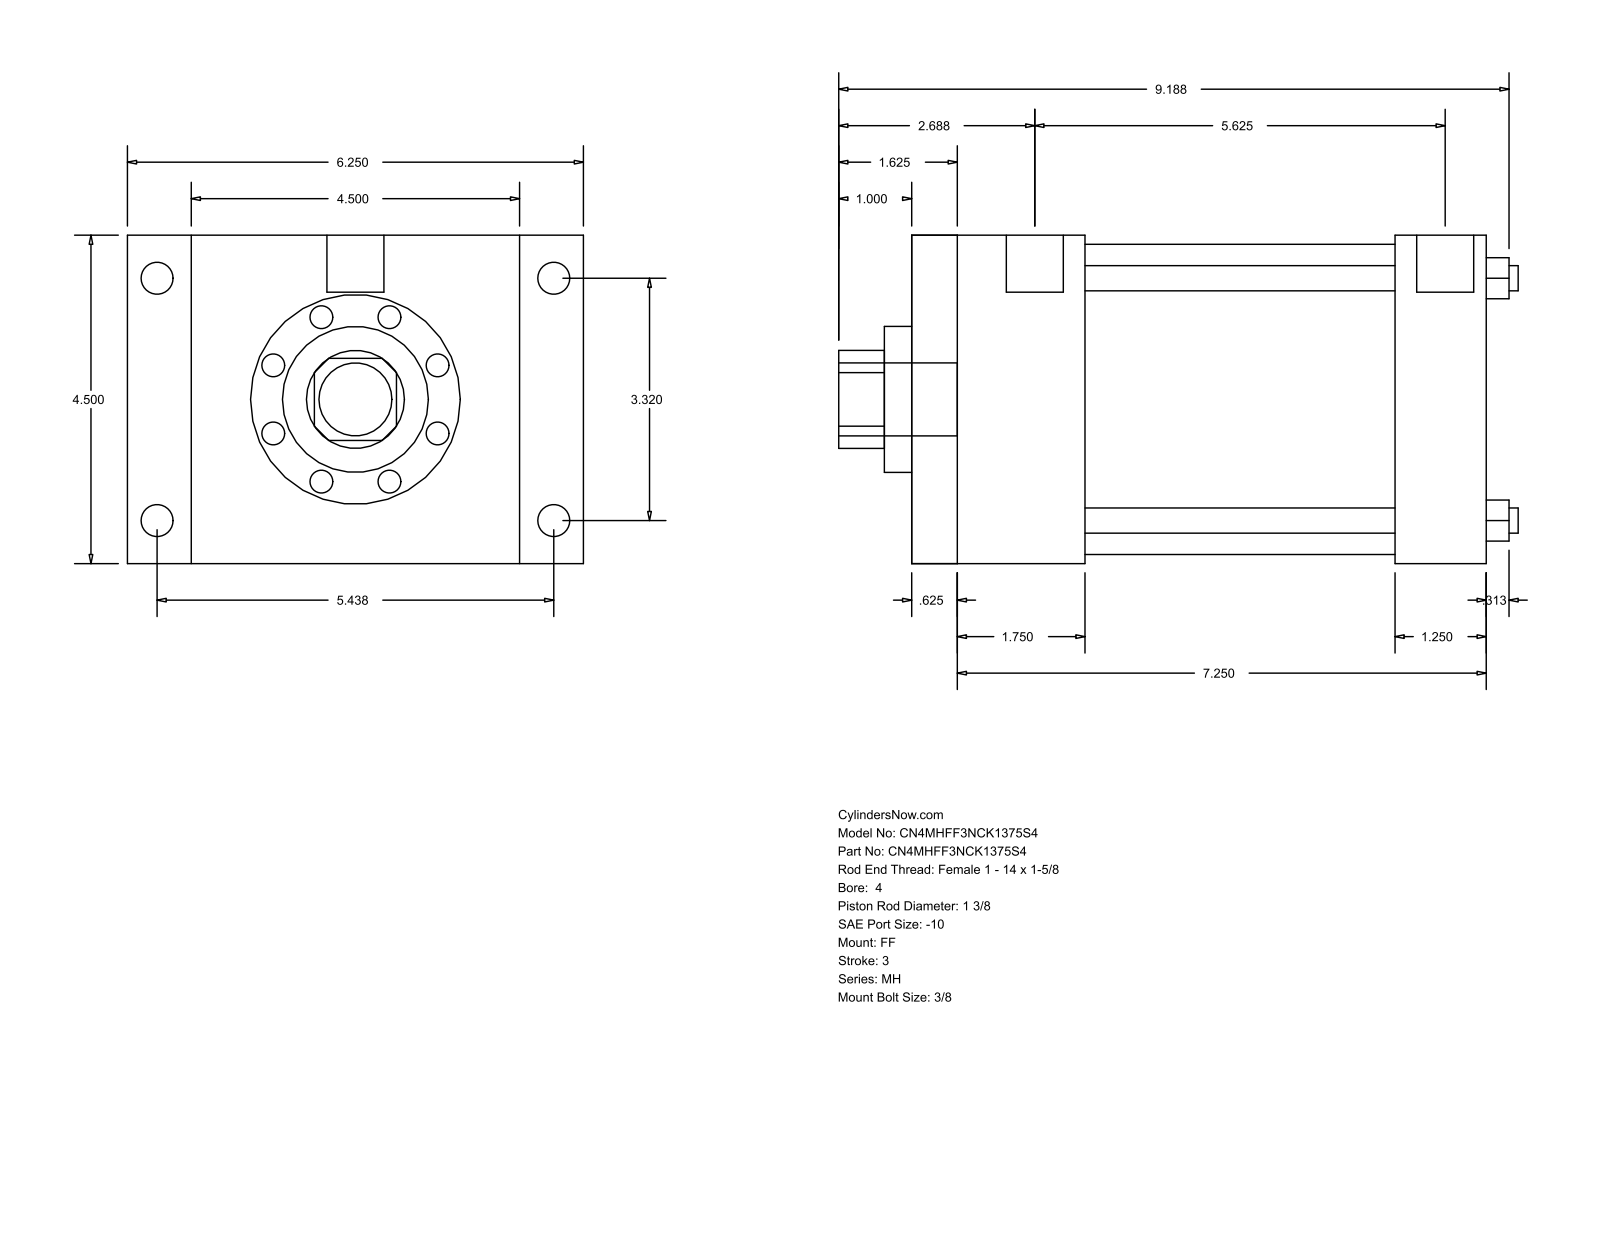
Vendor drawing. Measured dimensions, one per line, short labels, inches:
name: MH_FF__0400_1.375
written by: GSSL Pune (CONFIG_CONTROL_DESIGN)
unit: in
bodies: 0 solids, 92 faces (64 planar, 28 cylindrical, 0 other)
size: 9.313 × 6.25 × 4.5
holes: 4× ⌀0.345, 1× ⌀1.375, 1× ⌀2, 1× ⌀4.25
bosses: 4× ⌀0.438, 4× ⌀0.344, 2× ⌀0.781, 1× ⌀1
rounds: 1× R0.672
face distances: 4.5, 7.875, 0.625, 7.25, 2.375, 1.75, 5.5, 6.625, 6, 4.25
hole spacings: 2.347, 3.32, 4.695
